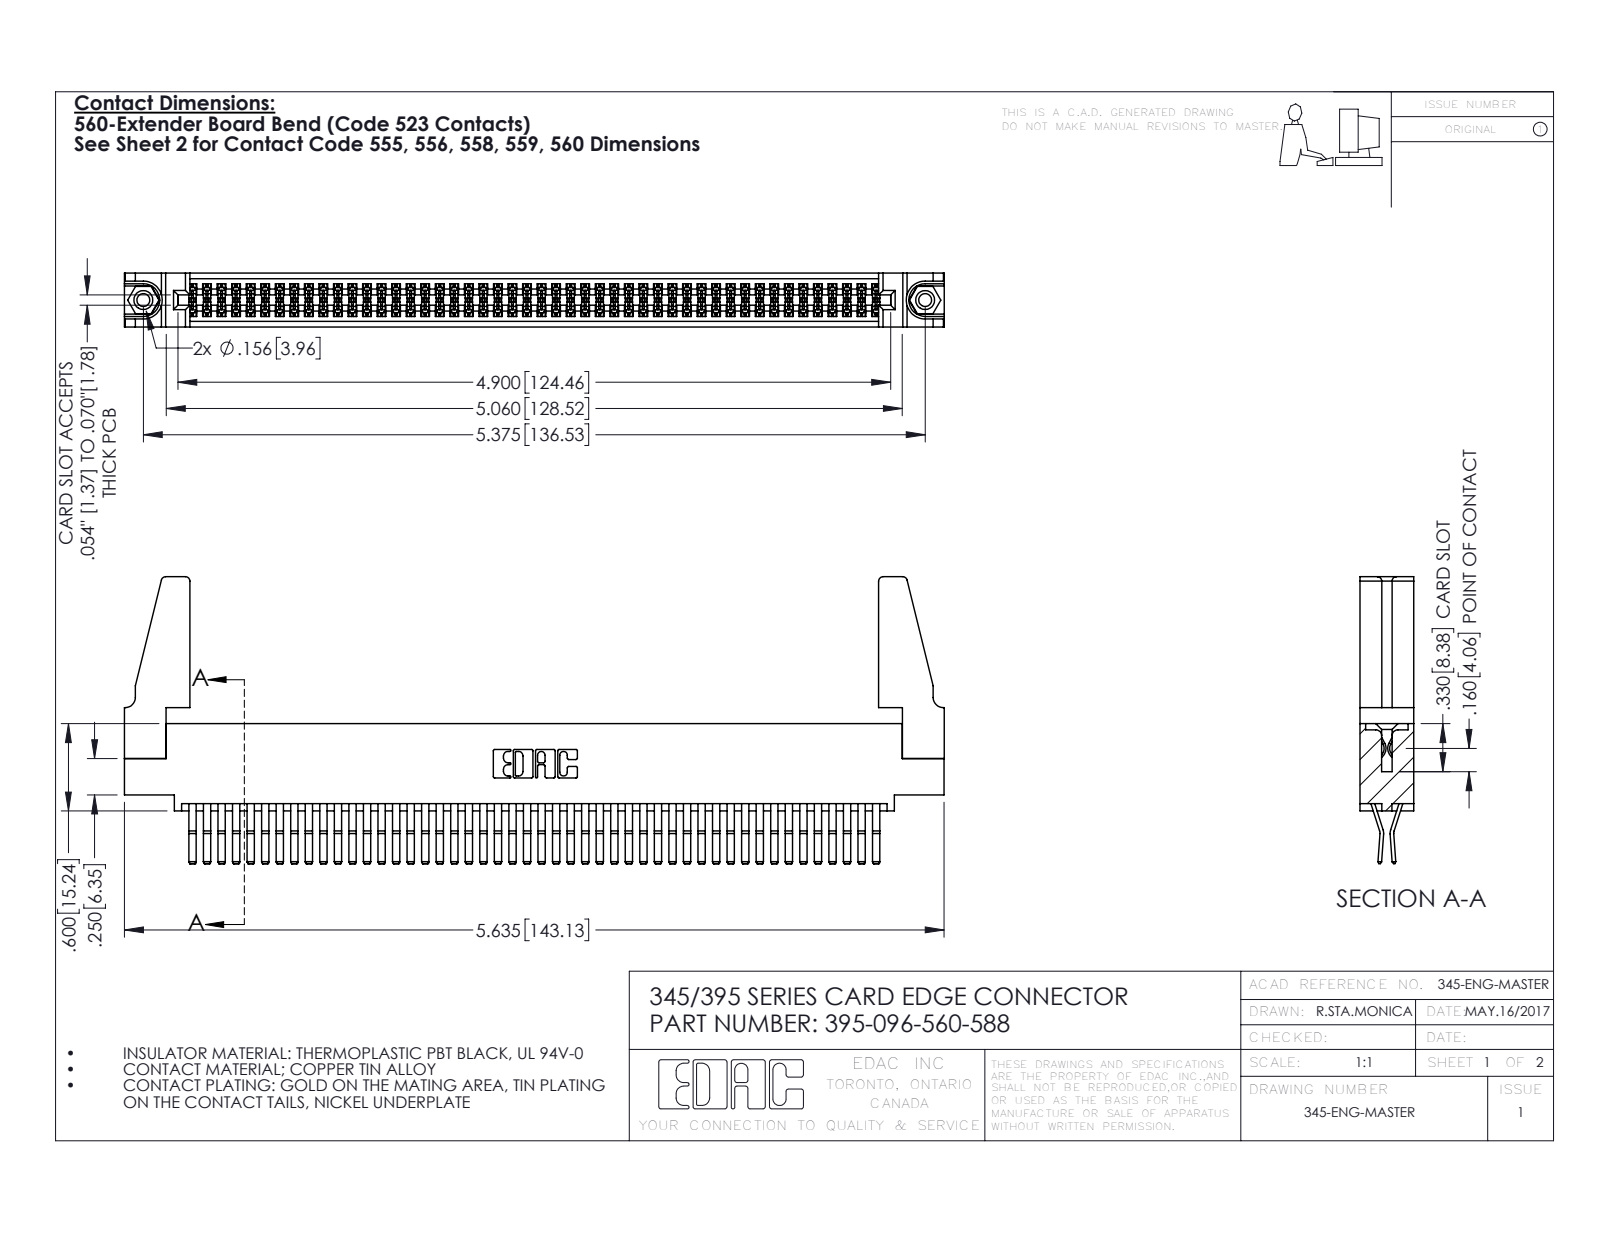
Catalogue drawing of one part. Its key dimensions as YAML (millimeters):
part_name: "345-250-001_345-250-001-102; 395-096-560-588; 345-292-001_560 Tail; 345-220-078_345-220-088 (+1 more)"
step_written_by: "SolidWorks 2016 (CONFIG_CONTROL_DESIGN)"
units: millimeters
bodies: {solids: 101, faces: 5246, planar: 3324, cylindrical: 1906, other: 16}
overall_size: [143.2, 50.1, 9.4]
volume: 17760
surface_area: 26410
round_holes:
  - {diameter: 2.3, count: 2}
  - {diameter: 3.2, count: 2}
  - {diameter: 4, count: 2}
  - {diameter: 1.6, count: 1}
round_bosses_or_shafts:
  - {diameter: 3.9, count: 2}
partial_cylinders:
  - {radius: 0.2, count: 145}
  - {radius: 0.3, count: 22}
  - {radius: 0.8, count: 8}
  - {radius: 0.2, count: 6}
  - {radius: 0.8, count: 6}
  - {radius: 0.7, count: 3}
  - {radius: 0.3, count: 2}
  - {radius: 0.4, count: 2}
face_to_face_distances: [1.8, 7.6, 0.6, 9.4, 5.1, 2.5, 6.9, 5.7, 4.4, 3.8]
hole_center_spacings: [6.9, 130.5, 136.5]
